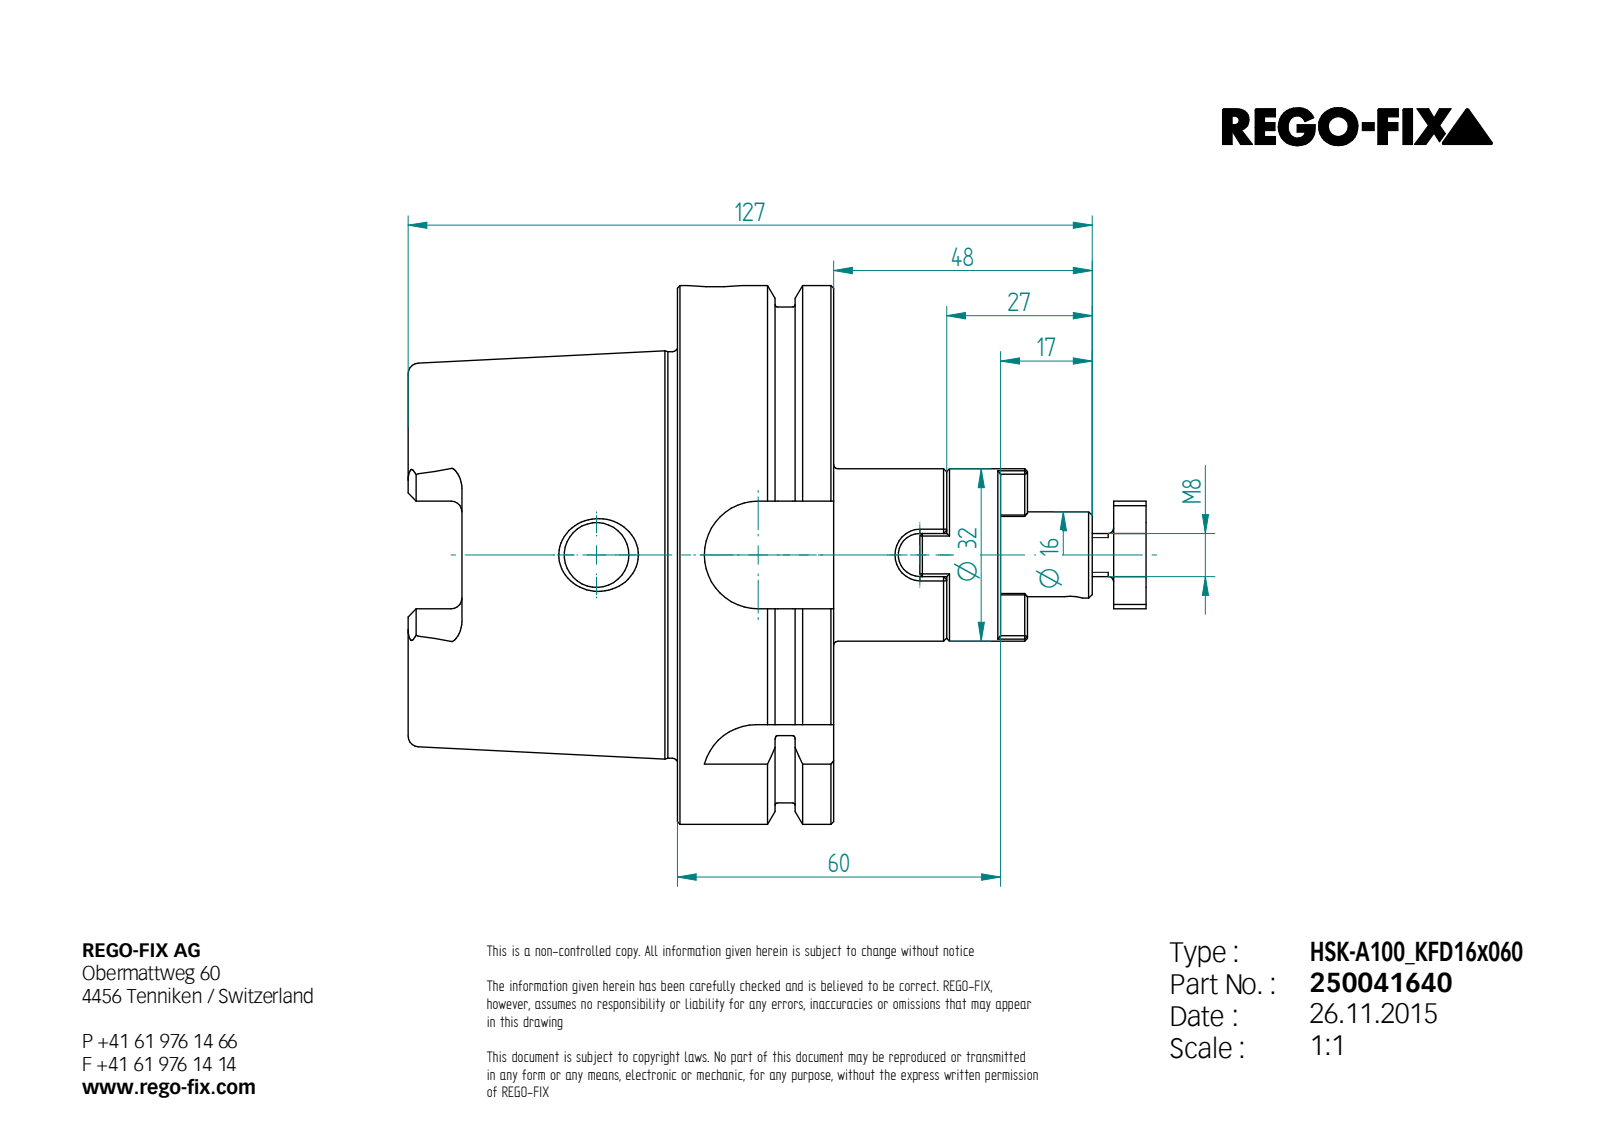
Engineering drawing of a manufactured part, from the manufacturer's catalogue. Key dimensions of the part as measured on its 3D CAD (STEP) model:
STEP written by: Unknown (AUTOMOTIVE_DESIGN)
Units: millimetres
Bodies: 3 solids, 255 faces (125 planar, 52 cylindrical, 78 other)
Overall size (bounding box): 137 × 100 × 100
Volume: 281 749 mm³ · Surface area: 58 988 mm²
Round holes (diameter × count): ⌀12 ×2, ⌀6.65 ×1, ⌀8.4 ×1, ⌀8.5 ×1, ⌀10 ×1, ⌀16 ×1, ⌀22.38 ×1, ⌀25 ×1, ⌀53 ×1, ⌀63 ×1
Round bosses / shafts (diameter × count): ⌀100 ×1, ⌀92 ×1, ⌀75.46 ×1, ⌀32 ×1, ⌀15.6 ×1, ⌀8 ×1
Partial cylindrical surfaces — rounded edges, fillets, slot ends (radius × count): R2 ×12, R4.88 ×4, R10 ×3, R4 ×1, R11 ×1
Main face-to-face distances: 29, 12.5, 16.5, 50, 100, 21, 62.5, 79, 37.5, 10
